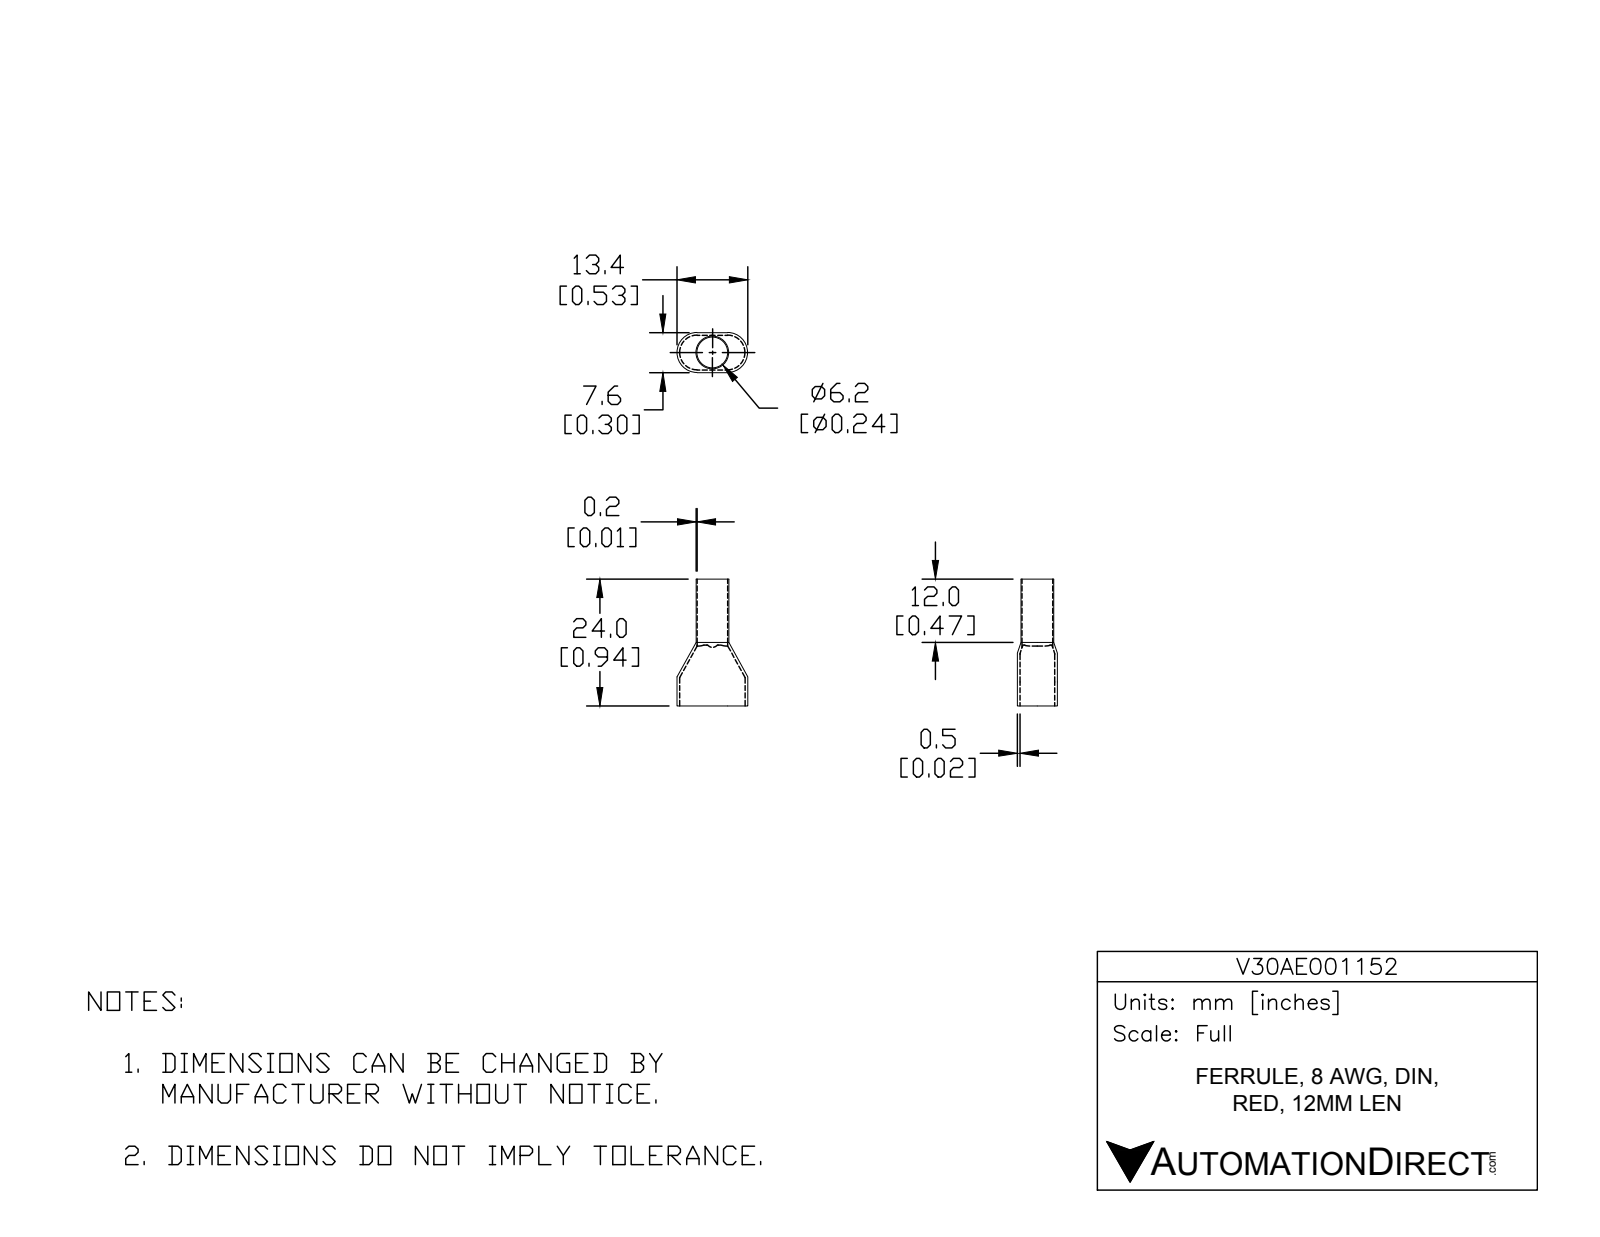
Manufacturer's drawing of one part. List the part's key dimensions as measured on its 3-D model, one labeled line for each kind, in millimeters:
Part name (STEP PRODUCT): V30AE001152
STEP written by: SolidWorks 2017 (AUTOMOTIVE_DESIGN)
Units: millimetres
Bodies: 2 solids, 38 faces (16 planar, 22 cylindrical, 0 other)
Overall size (bounding box): 24 × 13.4 × 7.6
Volume: 227 mm³ · Surface area: 1 215 mm²
Round holes (diameter × count): ⌀5.8 ×1
Round bosses / shafts (diameter × count): ⌀6.2 ×1
Partial cylindrical surfaces — rounded edges, fillets, slot ends (radius × count): R3.3 ×5, R3.8 ×5
Main face-to-face distances: 0.5, 7.1, 7.6, 6.6, 12, 24, 11.5, 12.5
